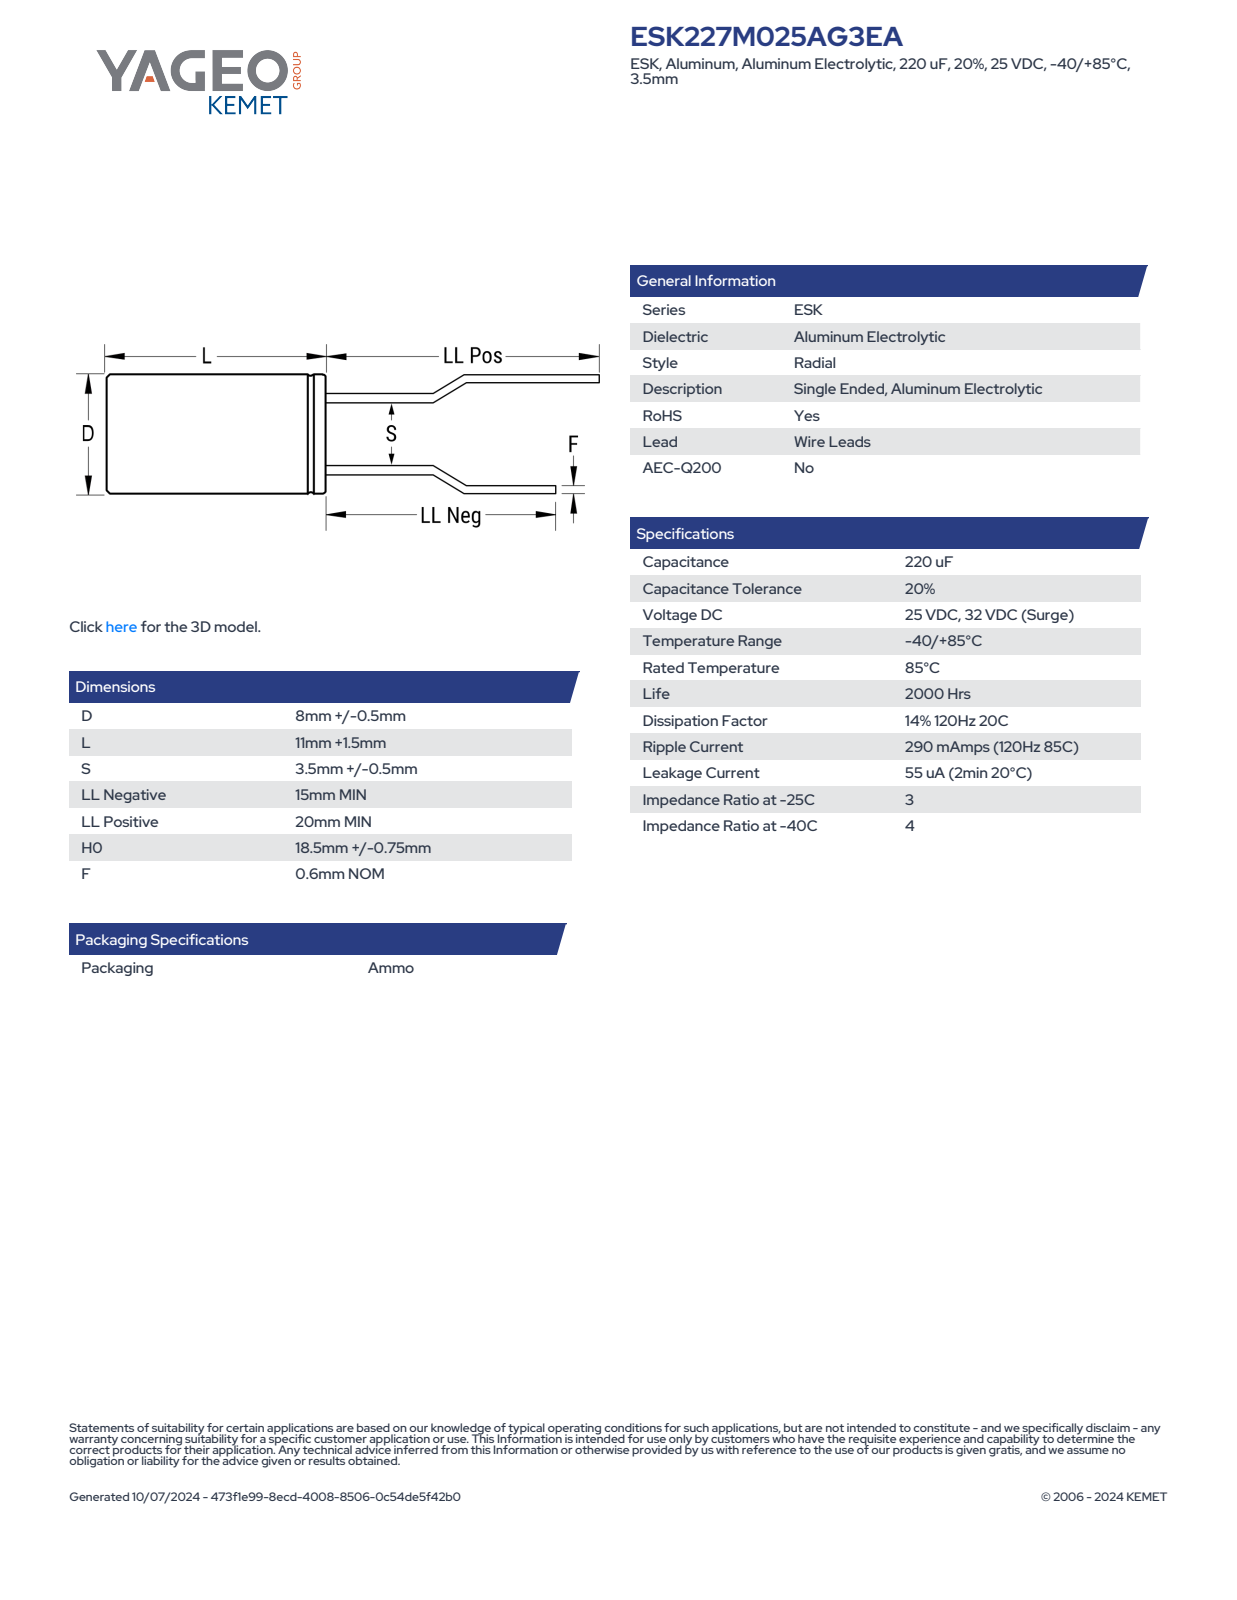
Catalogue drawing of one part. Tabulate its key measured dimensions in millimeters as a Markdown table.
| quantity | value |
| --- | --- |
| part name | CAR_KTRS_8X11_D8.5L12.5S3.5F0.6 |
| STEP written by | SolidWorks 2014 (AUTOMOTIVE_DESIGN) |
| units | millimeters |
| bodies | 4 solids, 73 faces (61 planar, 8 cylindrical, 4 other) |
| overall size | 32.51 × 8.5 × 8.5 |
| volume | 713 mm³ |
| surface area | 530 mm² |
| round bosses / shafts (diameter × count) | 0.6 × 2, 8.5 × 1 |
| main face-to-face distances | 12.5, 12.51, 27.51, 32.51, 27.5, 32.5, 15, 20, 5, 1.01 |
